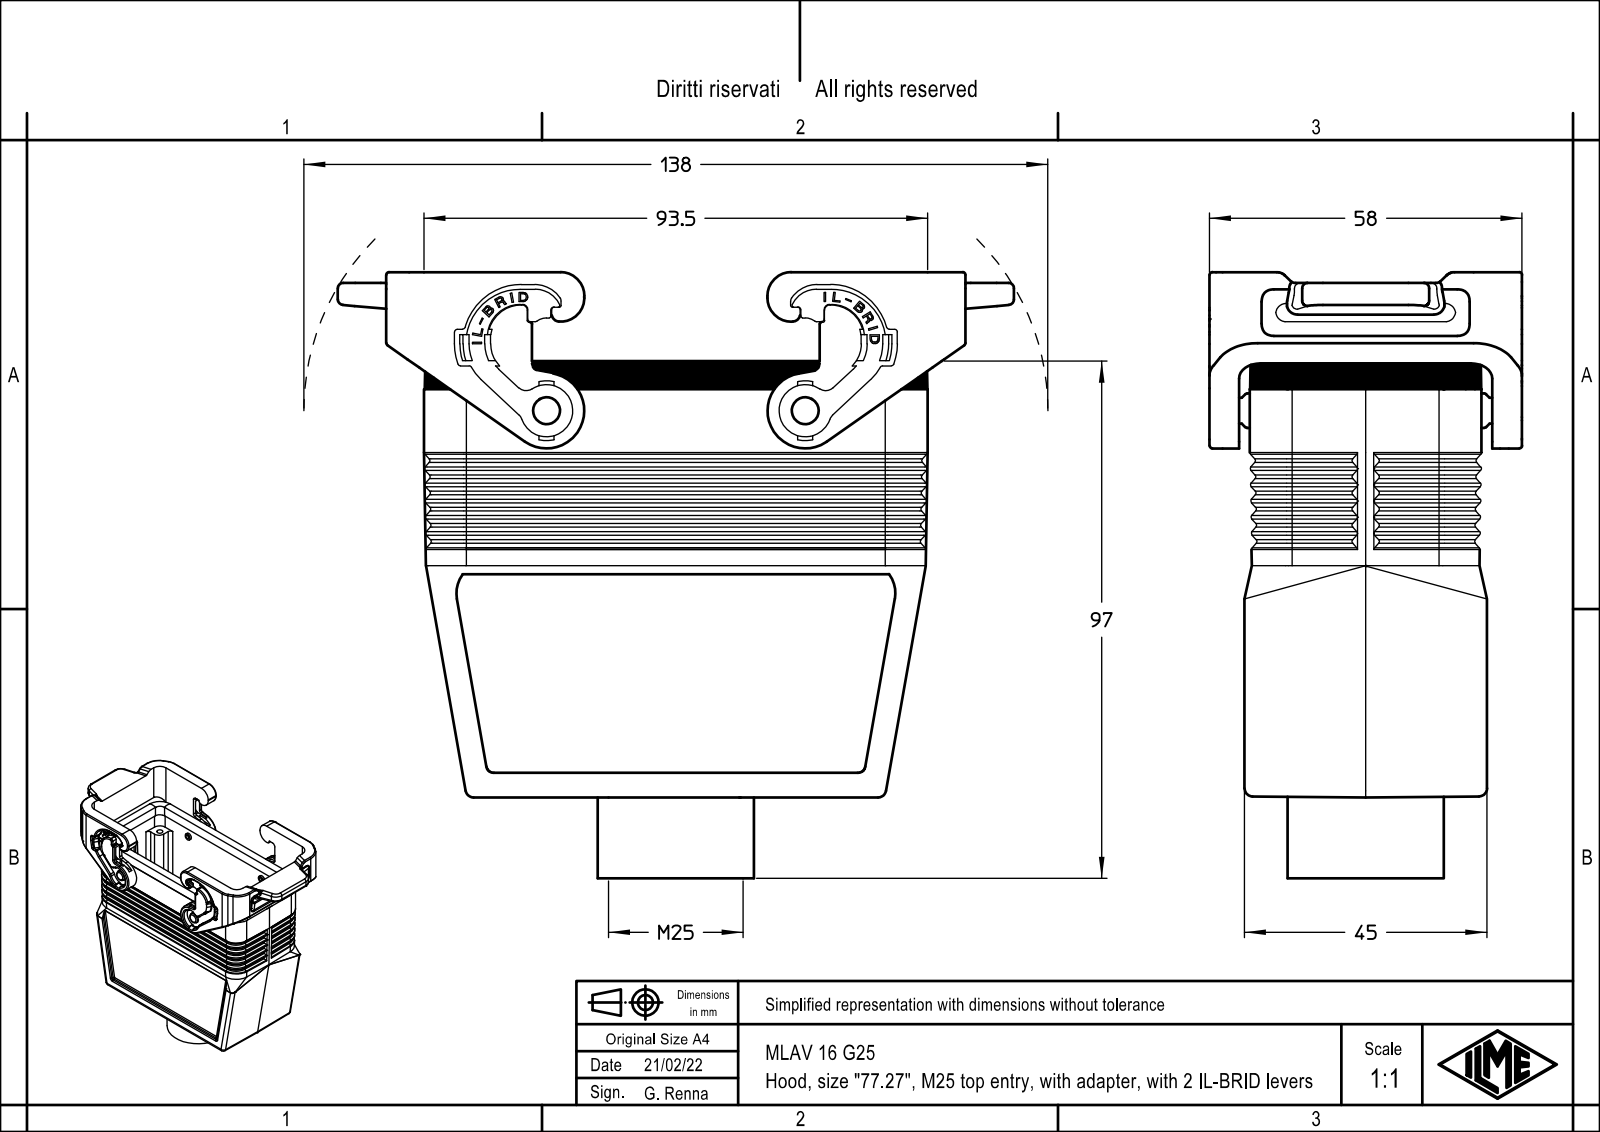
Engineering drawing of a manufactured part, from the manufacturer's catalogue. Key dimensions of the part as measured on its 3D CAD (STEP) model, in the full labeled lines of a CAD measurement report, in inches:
Part name (STEP PRODUCT): MLAV_16_G25
STEP written by: Creo Elements/Direct Modeling 20.1B 02-Apr-2019 (C) Parametric Technology GmbH (AUTOMOTIVE_DESIGN)
Units: inches
Bodies: 1 solid, 1611 faces (1031 planar, 395 cylindrical, 185 other)
Overall size (bounding box): 4.941 × 4.427 × 2.283
Volume: 7.582 in³ · Surface area: 99.32 in²
Round holes (diameter × count): ⌀0.108 ×4, ⌀0.787 ×1, ⌀0.984 ×1
Round bosses / shafts (diameter × count): ⌀0.268 ×2, ⌀0.189 ×2, ⌀1.142 ×1
Partial cylindrical surfaces — rounded edges, fillets, slot ends (radius × count): R0.02 ×104, R0.039 ×46, R0.118 ×20, R0.276 ×16, R0.013 ×15, R0.059 ×14, R0.012 ×8, R0.079 ×8
Main face-to-face distances: 1.545, 0.148, 0.079, 0.039, 0.226, 0.187, 1.693, 1.772, 1.358, 1.506
Hole centre spacings: 1.615, 1.063, 3.051, 3.231
